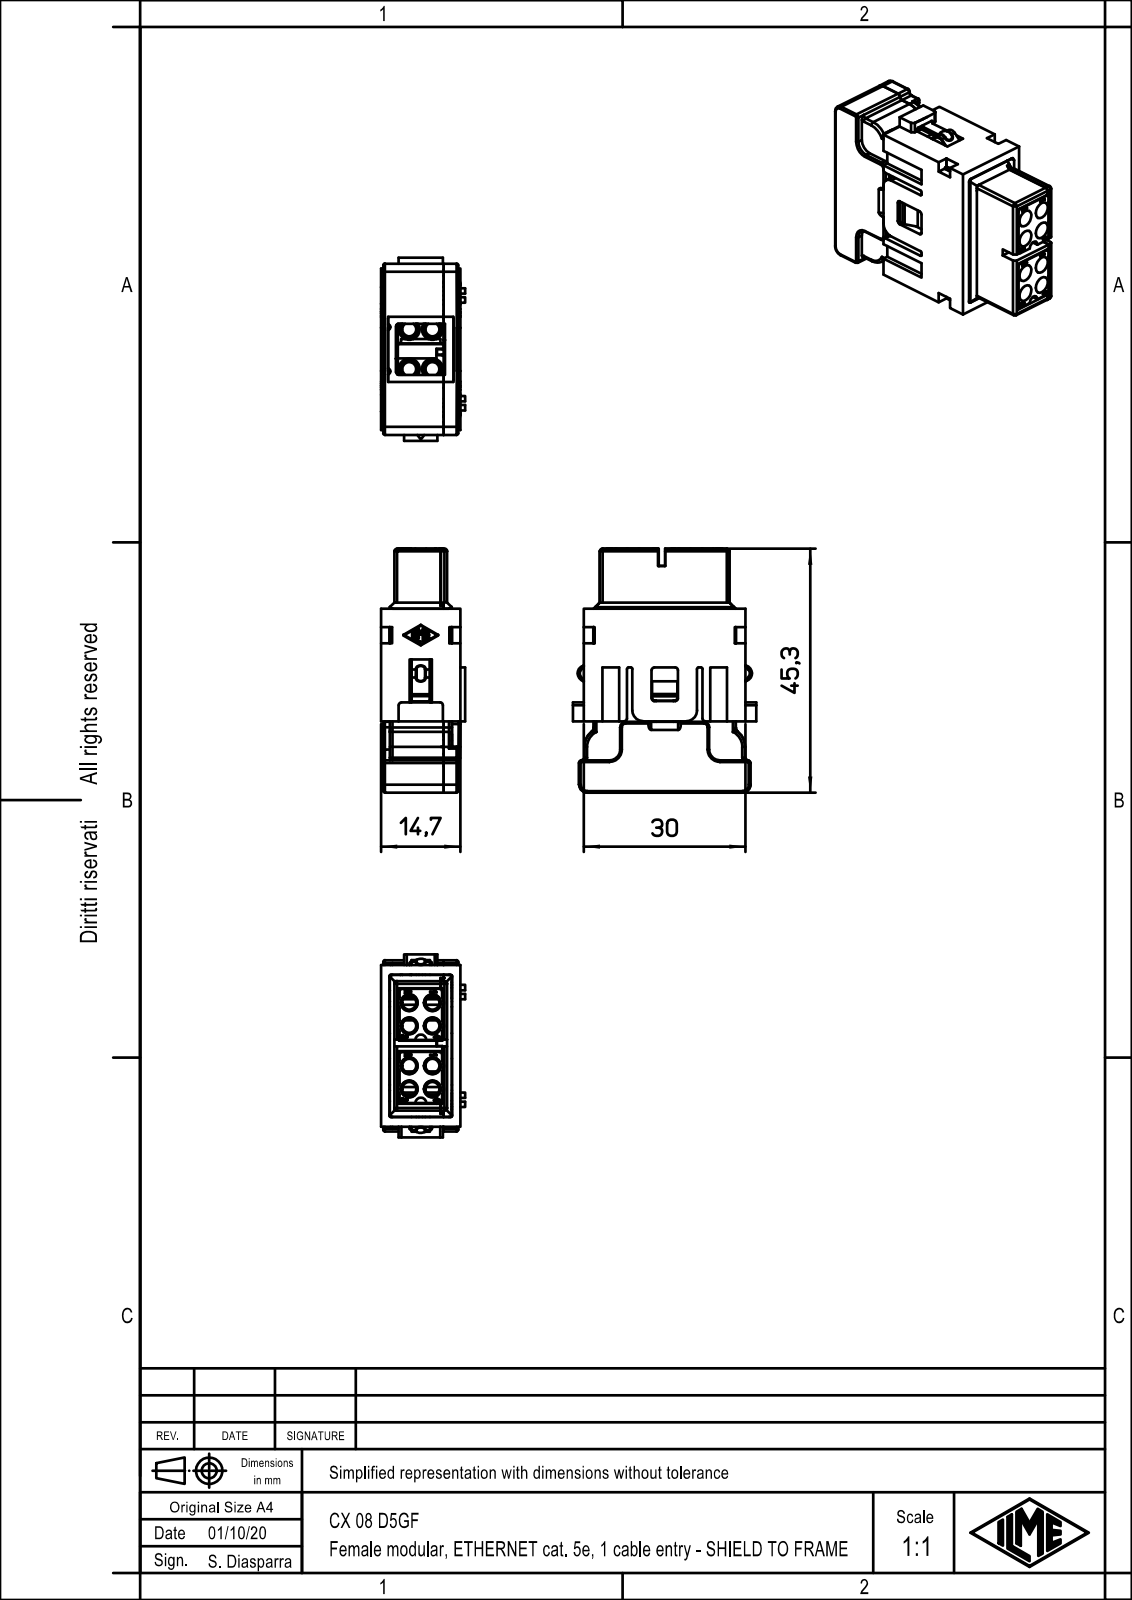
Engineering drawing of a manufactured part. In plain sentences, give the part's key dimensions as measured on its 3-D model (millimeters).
The part is named "CX 08 D5GF". Its 3-D file was written by "Creo Elements/Direct Modeling 20.1B 02-Apr-2019 (C) Parametric Technology GmbH (AUTOMOTIVE_DESIGN)". It is 1 solid with 656 faces: 396 planar, 179 cylindrical and 81 other. Overall it measures 45.3 by 34 by 15.6 millimeters. Its volume is 15 196 cubic millimeters and its surface area 10 739 square millimeters. Round holes: 2 of diameter 2.6, 2 of diameter 5. Round bosses or shafts: 2 of diameter 4.7, 2 of diameter 1.9. Partial cylindrical surfaces (rounded edges, fillets, slot ends): 57 of radius 0.5, 36 of radius 0.3, 10 of radius 1, 6 of radius 2, 4 of radius 0.2, 4 of radius 0.4, 4 of radius 0.65, 4 of radius 2.15. The main face-to-face distances are 0.9, 10.65, 1.6, 13.1, 13.15, 1.55, 11.55, 1.15, 1.2, 12.1. The hole center spacings are 22.6.
